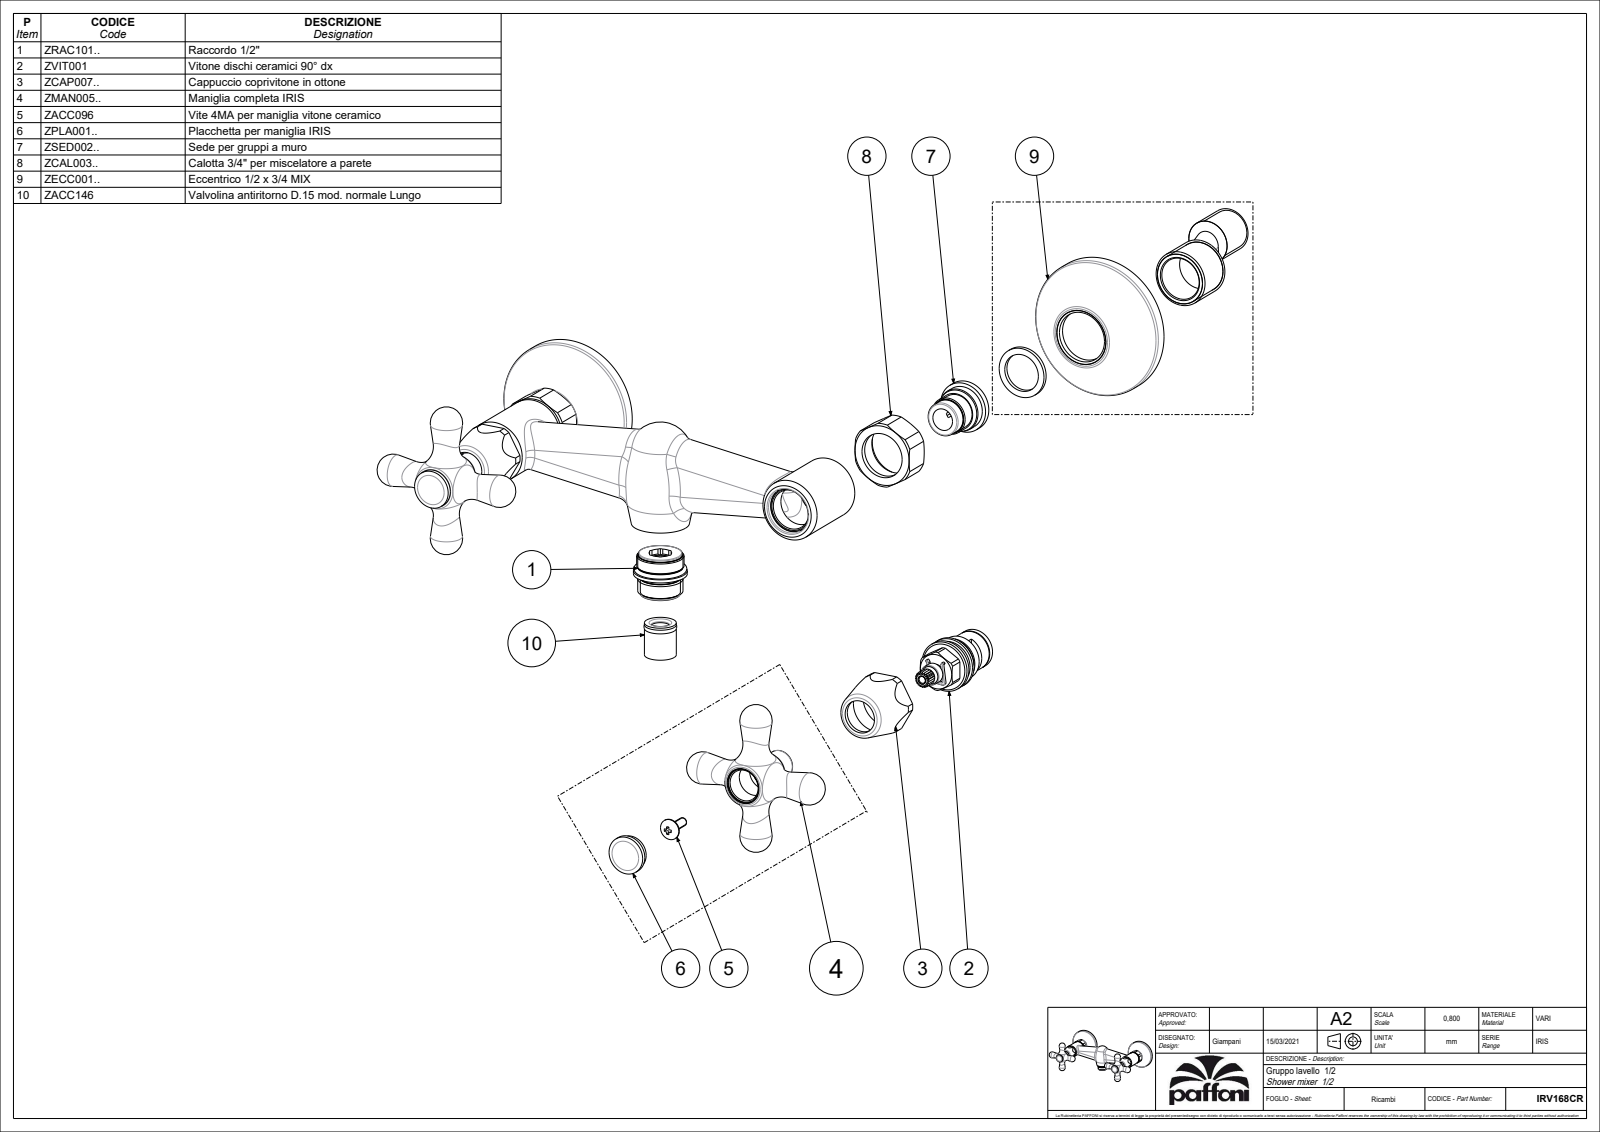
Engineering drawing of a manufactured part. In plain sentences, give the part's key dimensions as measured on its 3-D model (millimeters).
The part is named "IRV168CR". Its 3-D file was written by "CREO PARAMETRIC BY PTC INC, 2020044 (CONFIG_CONTROL_DESIGN)". It is 3 solids with 605 faces: 205 planar, 114 cylindrical and 286 other. Overall it measures 230 by 131.2 by 73.5 millimeters. Its volume is 238 668 cubic millimeters and its surface area 78 717 square millimeters. Round holes: 2 of diameter 8, 2 of diameter 10.5, 2 of diameter 15.7, 2 of diameter 19, 2 of diameter 21.3, 2 of diameter 22, 2 of diameter 23, 1 of diameter 15.1, 1 of diameter 21. Round bosses or shafts: 3 of diameter 18, 2 of diameter 65.5, 2 of diameter 29, 2 of diameter 20.5, 2 of diameter 17.7, 2 of diameter 16, 2 of diameter 13.5, 1 of diameter 25. Partial cylindrical surfaces (rounded edges, fillets, slot ends): 4 of radius 6.5, 4 of radius 10, 2 of radius 12.5, 2 of radius 15.5, 1 of radius 5.25, 1 of radius 12. The main face-to-face distances are 16.5, 3.5, 10, 26.5, 8.5, 28.5, 1.5, 12, 34, 20. The hole center spacings are 158.
